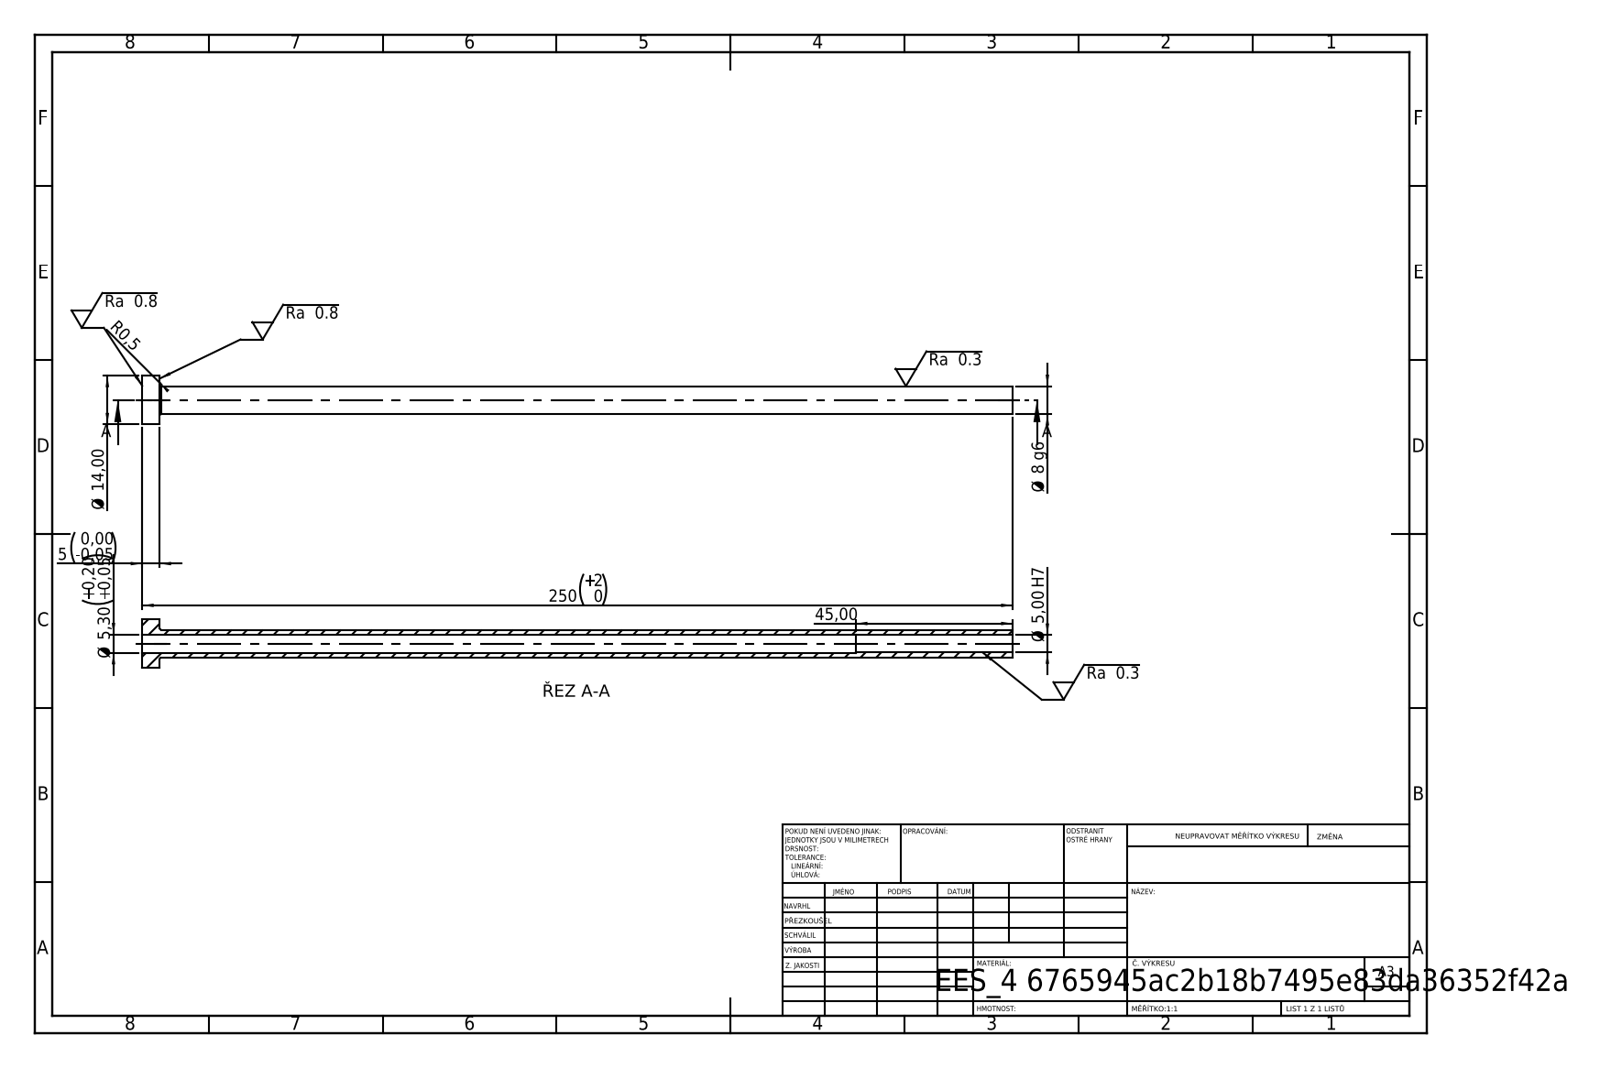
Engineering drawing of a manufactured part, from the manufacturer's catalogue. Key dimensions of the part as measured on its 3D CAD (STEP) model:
STEP written by: SolidWorks 2019 (CONFIG_CONTROL_DESIGN)
Units: millimetres
Bodies: 1 solid, 14 faces (4 planar, 8 cylindrical, 2 other)
Overall size (bounding box): 250 × 14 × 14
Volume: 7 680 mm³ · Surface area: 10 761 mm²
Round holes (diameter × count): ⌀5 ×1, ⌀5.3 ×1
Round bosses / shafts (diameter × count): ⌀14 ×1, ⌀8 ×1
Main face-to-face distances: 5, 250, 245, 205, 200, 45
